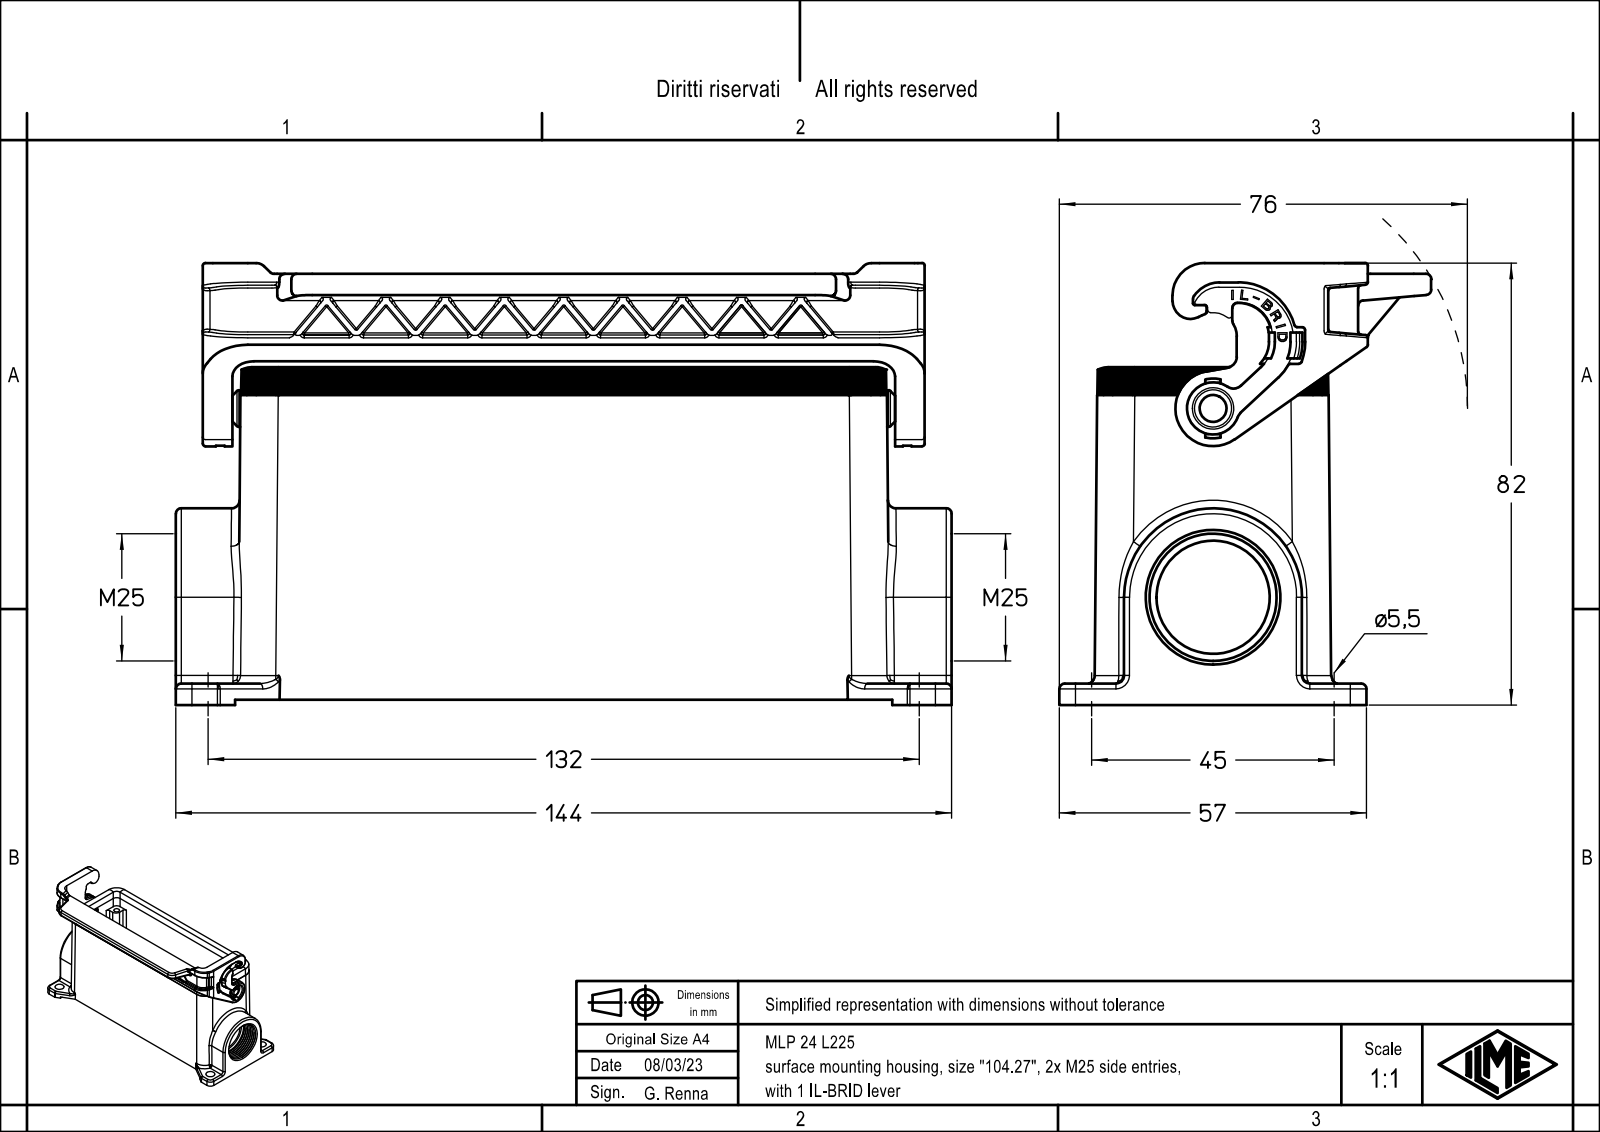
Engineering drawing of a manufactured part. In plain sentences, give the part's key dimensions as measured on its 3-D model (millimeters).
The part is named "MLP 24 L225". Its 3-D file was written by "Creo Elements/Direct Modeling 20.1B 02-Apr-2019 (C) Parametric Technology GmbH (AUTOMOTIVE_DESIGN)". It is 1 solid with 1128 faces: 651 planar, 299 cylindrical and 178 other. Overall it measures 144 by 82 by 69 millimeters. Its volume is 131 061 cubic millimeters and its surface area 71 082 square millimeters. Round holes: 4 of diameter 3, 4 of diameter 3.5, 4 of diameter 5.5, 1 of diameter 3.25, 1 of diameter 5.4, 1 of diameter 7.7, 1 of diameter 21, 1 of diameter 23.6. Round bosses or shafts: 1 of diameter 6.9, 1 of diameter 6.8, 1 of diameter 5.2, 1 of diameter 3.2. Partial cylindrical surfaces (rounded edges, fillets, slot ends): 27 of radius 0.1, 21 of radius 1, 16 of radius 3, 15 of radius 0.2, 13 of radius 1.5, 11 of radius 0.5, 10 of radius 7, 9 of radius 2. The main face-to-face distances are 3, 79, 76, 10.5, 133.5, 1, 4, 38.9, 5, 5.5. The hole center spacings are 16.64, 38.63, 118.34, 123.37, 27, 45, 104, 107.45.
